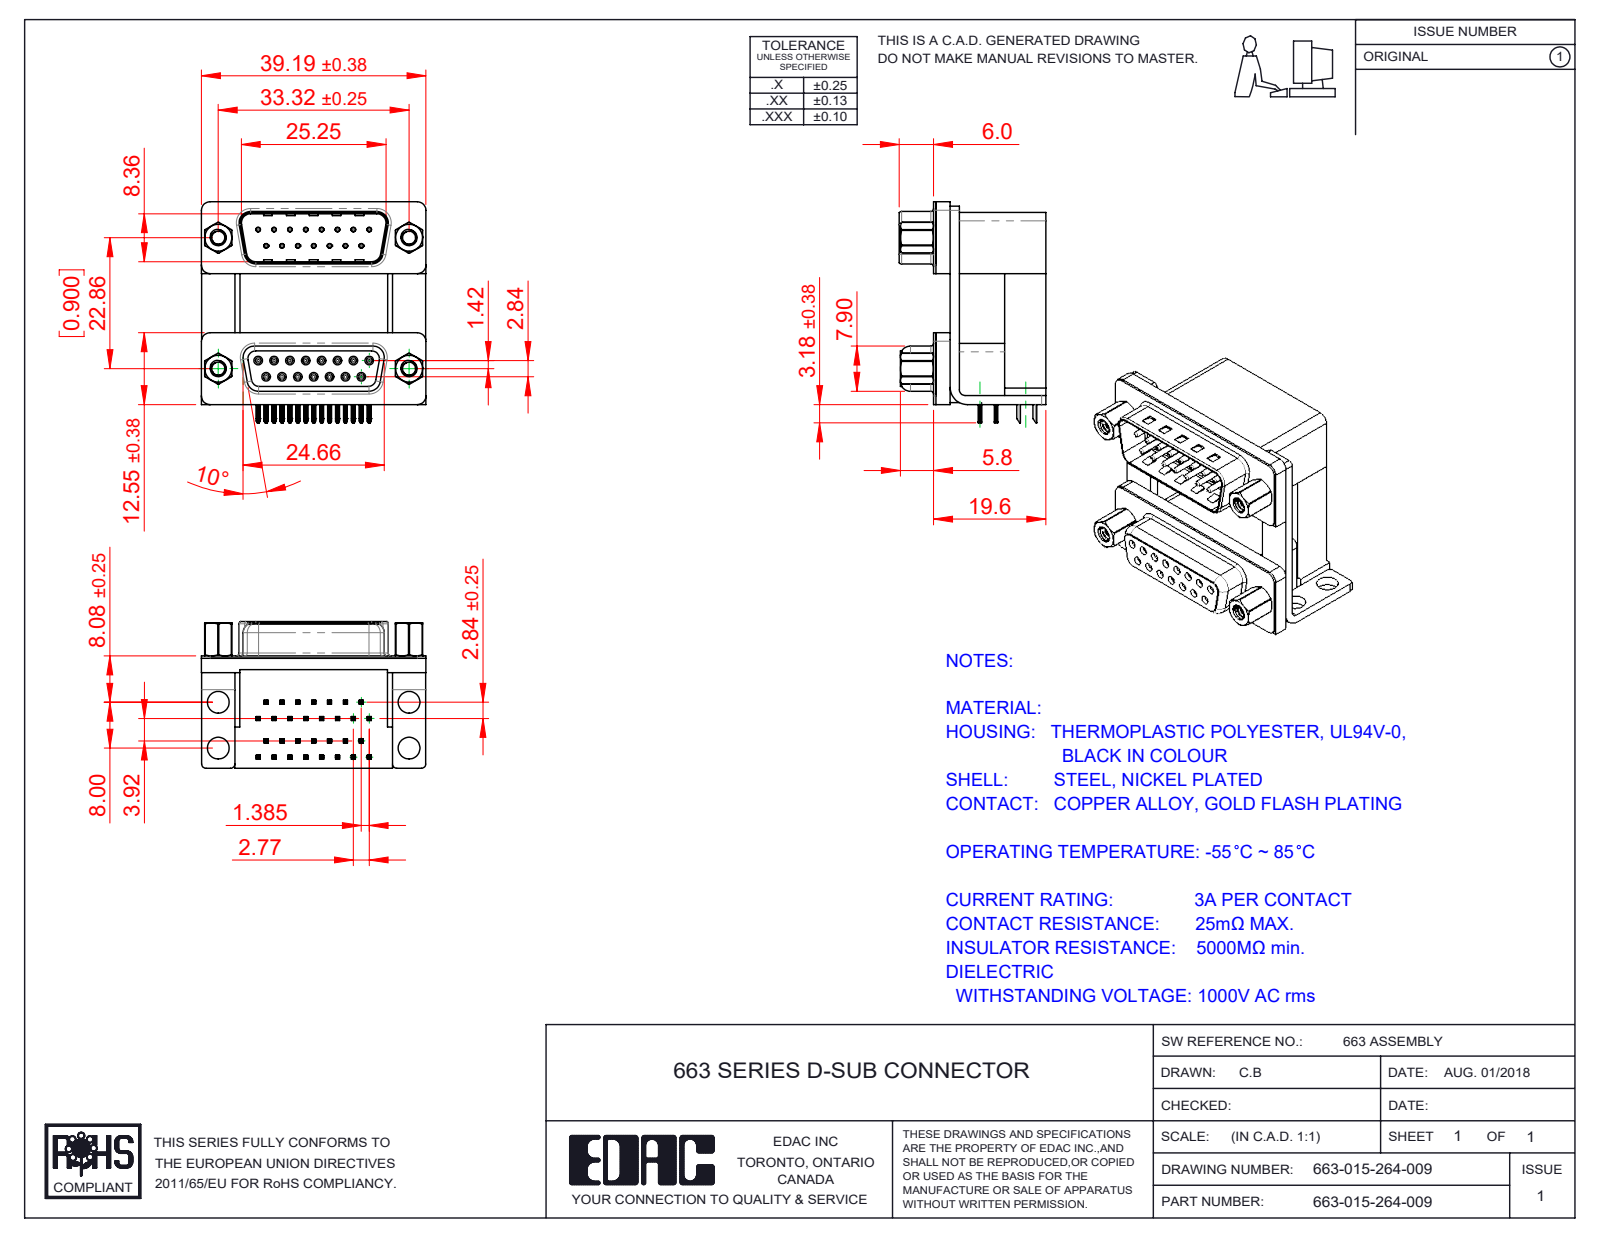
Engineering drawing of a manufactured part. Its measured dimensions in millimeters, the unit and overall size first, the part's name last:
Units: millimetres
Overall size (bounding box): 39.19 × 38.59 × 25.6
Round holes (diameter × count): ⌀0.8 ×30, ⌀0.35 ×15, ⌀0.9 ×15, ⌀2.26 ×4, ⌀2.29 ×4, ⌀3.5 ×4, ⌀3.8 ×4, ⌀4 ×4, ⌀4.8 ×4, ⌀5 ×4
Round bosses / shafts (diameter × count): ⌀1.2 ×15, ⌀0.75 ×15, ⌀4.9 ×4, ⌀4.75 ×4, ⌀3.9 ×4, ⌀2.79 ×4
Partial cylindrical surfaces — rounded edges, fillets, slot ends (radius × count): R0.1 ×120, R0.15 ×60, R0.25 ×60, R0.12 ×30, R0.35 ×30, R1.5 ×16, R0.34 ×15, R0.5 ×12
Main face-to-face distances: 0.4, 19.2, 12, 7.2, 16.7, 9.5, 2.5, 12.4, 10.7, 22.86
Hole centre spacings: 3.16, 23.03, 2.77, 23.52, 5.54, 8.31, 22.86, 24.32
Volume: 16 404 mm³ · Surface area: 18 372 mm²
Bodies: 45 solids, 4164 faces (2059 planar, 1158 cylindrical, 947 other)
Part name (STEP PRODUCT): 663 Housing Upper_15 Contacts H; 663 Shell Receptacle_15 Contacts; 663 Contact Bottom Upper_H; 663 Shell Plug_15 Contacts (+8 more)
STEP written by: SolidWorks 2020 (CONFIG_CONTROL_DESIGN)
